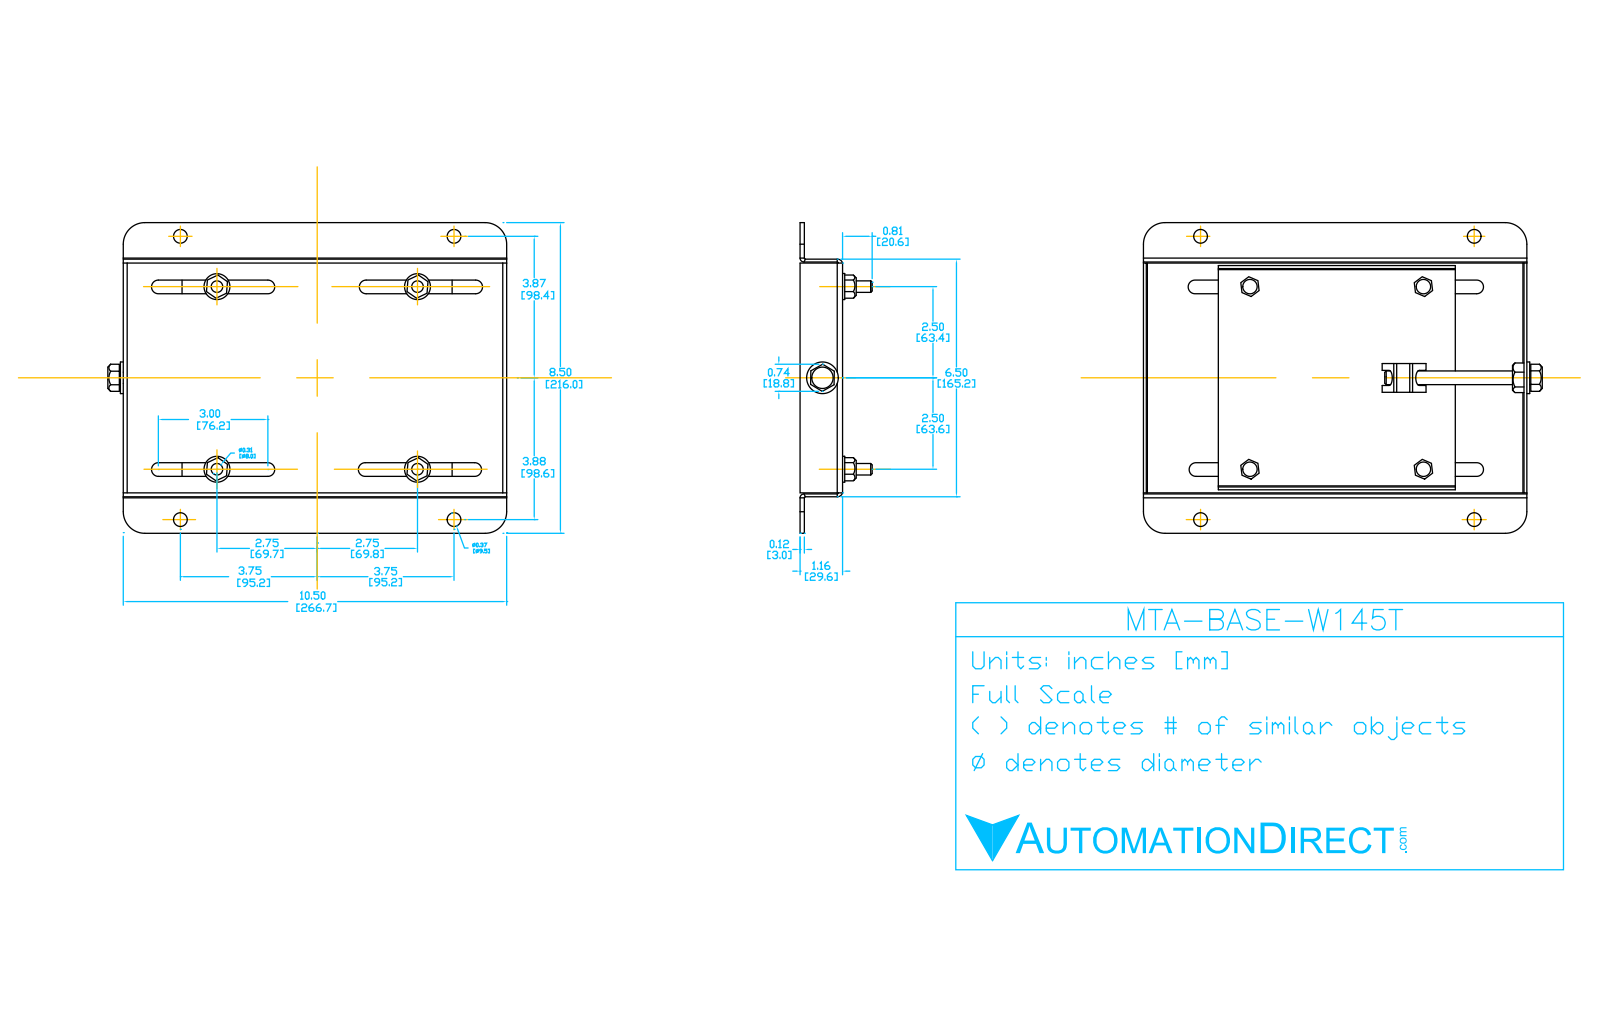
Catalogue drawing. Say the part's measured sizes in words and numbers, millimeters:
The part is named "W145T". Its 3-D file was written by "SolidWorks 2017 (AUTOMOTIVE_DESIGN)". It is 18 solids with 306 faces: 157 planar, 101 cylindrical and 48 other. Overall it measures 278.2 by 215.9 by 49 millimeters. Its volume is 310 900 cubic millimeters and its surface area 238 300 square millimeters. Round holes: 6 of diameter 8, 5 of diameter 9, 4 of diameter 9.5, 1 of diameter 9.5, 1 of diameter 13. Round bosses or shafts: 5 of diameter 18. Partial cylindrical surfaces (rounded edges, fillets, slot ends): 10 of radius 0.7, 8 of radius 4.7, 6 of radius 3.7, 4 of radius 1, 4 of radius 15, 2 of radius 2.2, 2 of radius 2.7, 2 of radius 5.3. The main face-to-face distances are 3, 2, 5, 25.6, 28.6, 22.6, 20.6, 23.6, 162.1, 263.7. The hole center spacings are 127, 0.7, 139, 139.7, 188.3, 188.8, 190.5, 196.9.
